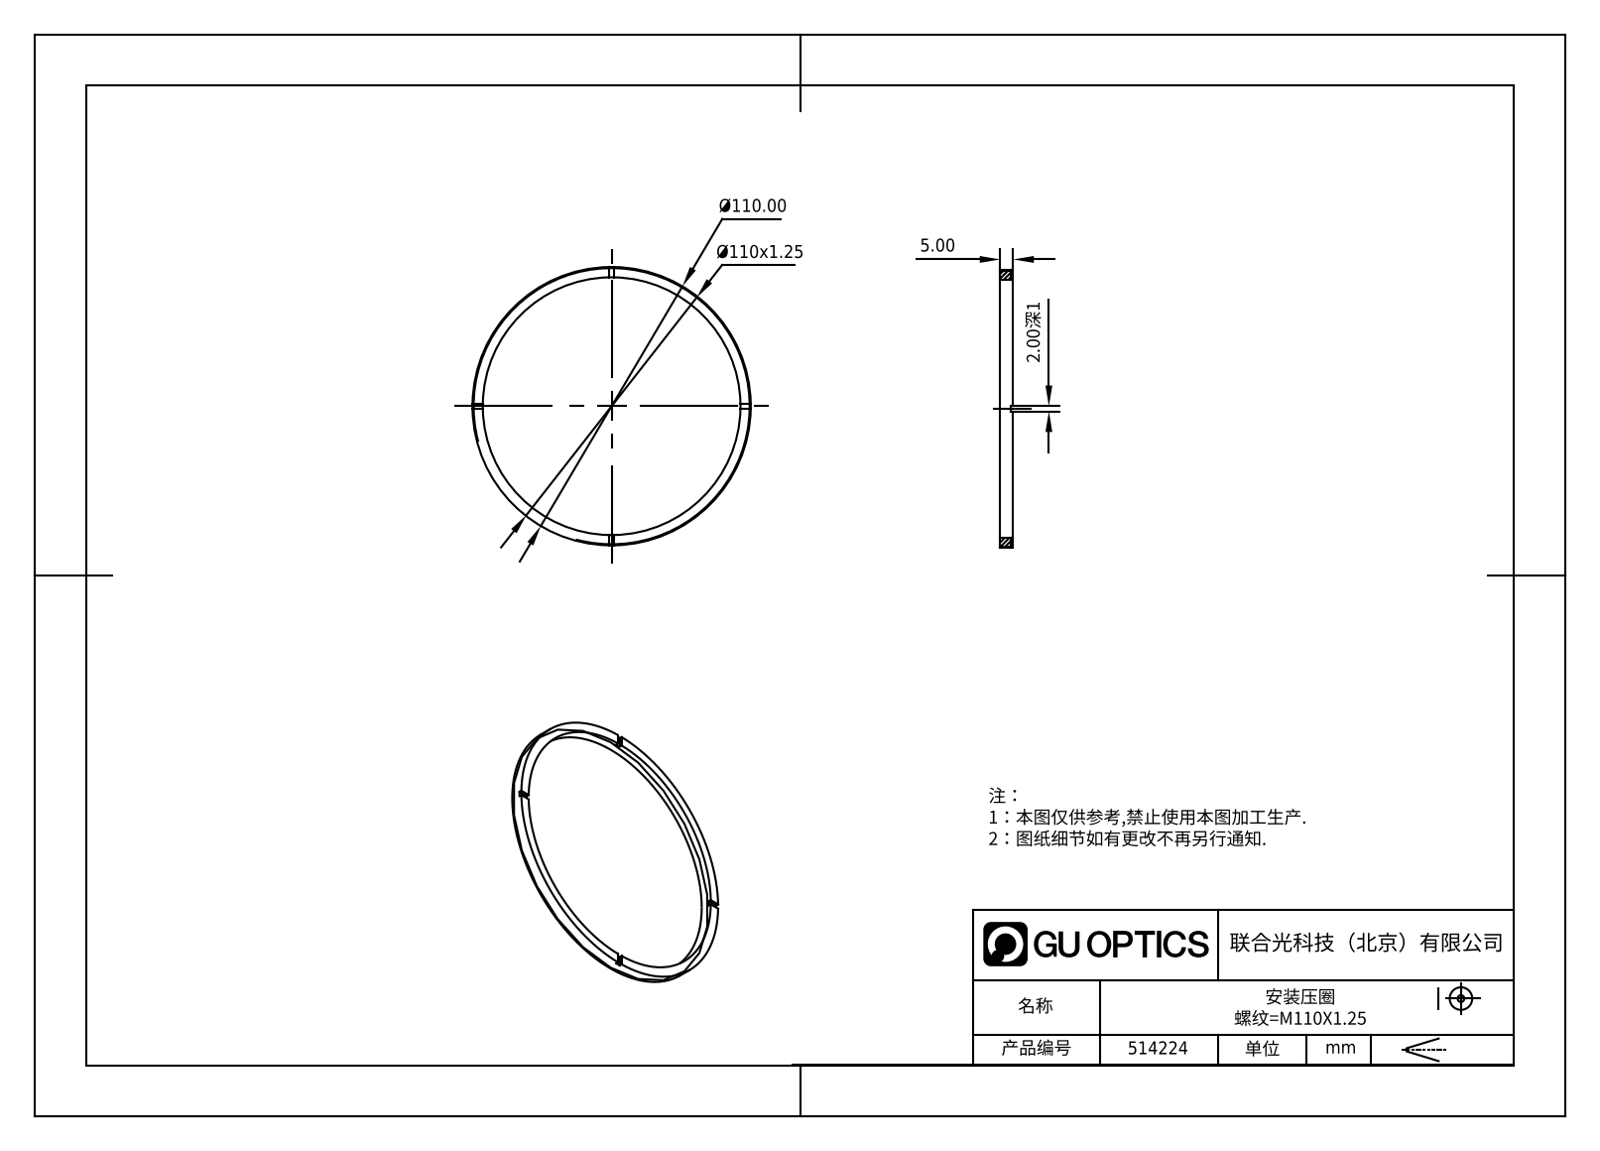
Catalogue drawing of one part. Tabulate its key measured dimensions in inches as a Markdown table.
| quantity | value |
| --- | --- |
| part name | 514224 |
| STEP written by | SolidWorks 2020 (CONFIG_CONTROL_DESIGN) |
| units | inches |
| bodies | 1 solid, 21 faces (17 planar, 4 cylindrical, 0 other) |
| overall size | 4.331 × 4.331 × 0.217 |
| volume | 0.551 in³ |
| surface area | 10.77 in² |
| round holes (diameter × count) | 3.937 × 1 |
| round bosses / shafts (diameter × count) | 4.331 × 1 |
| main face-to-face distances | 0.217, 0.177, 0.039, 0.079 |
